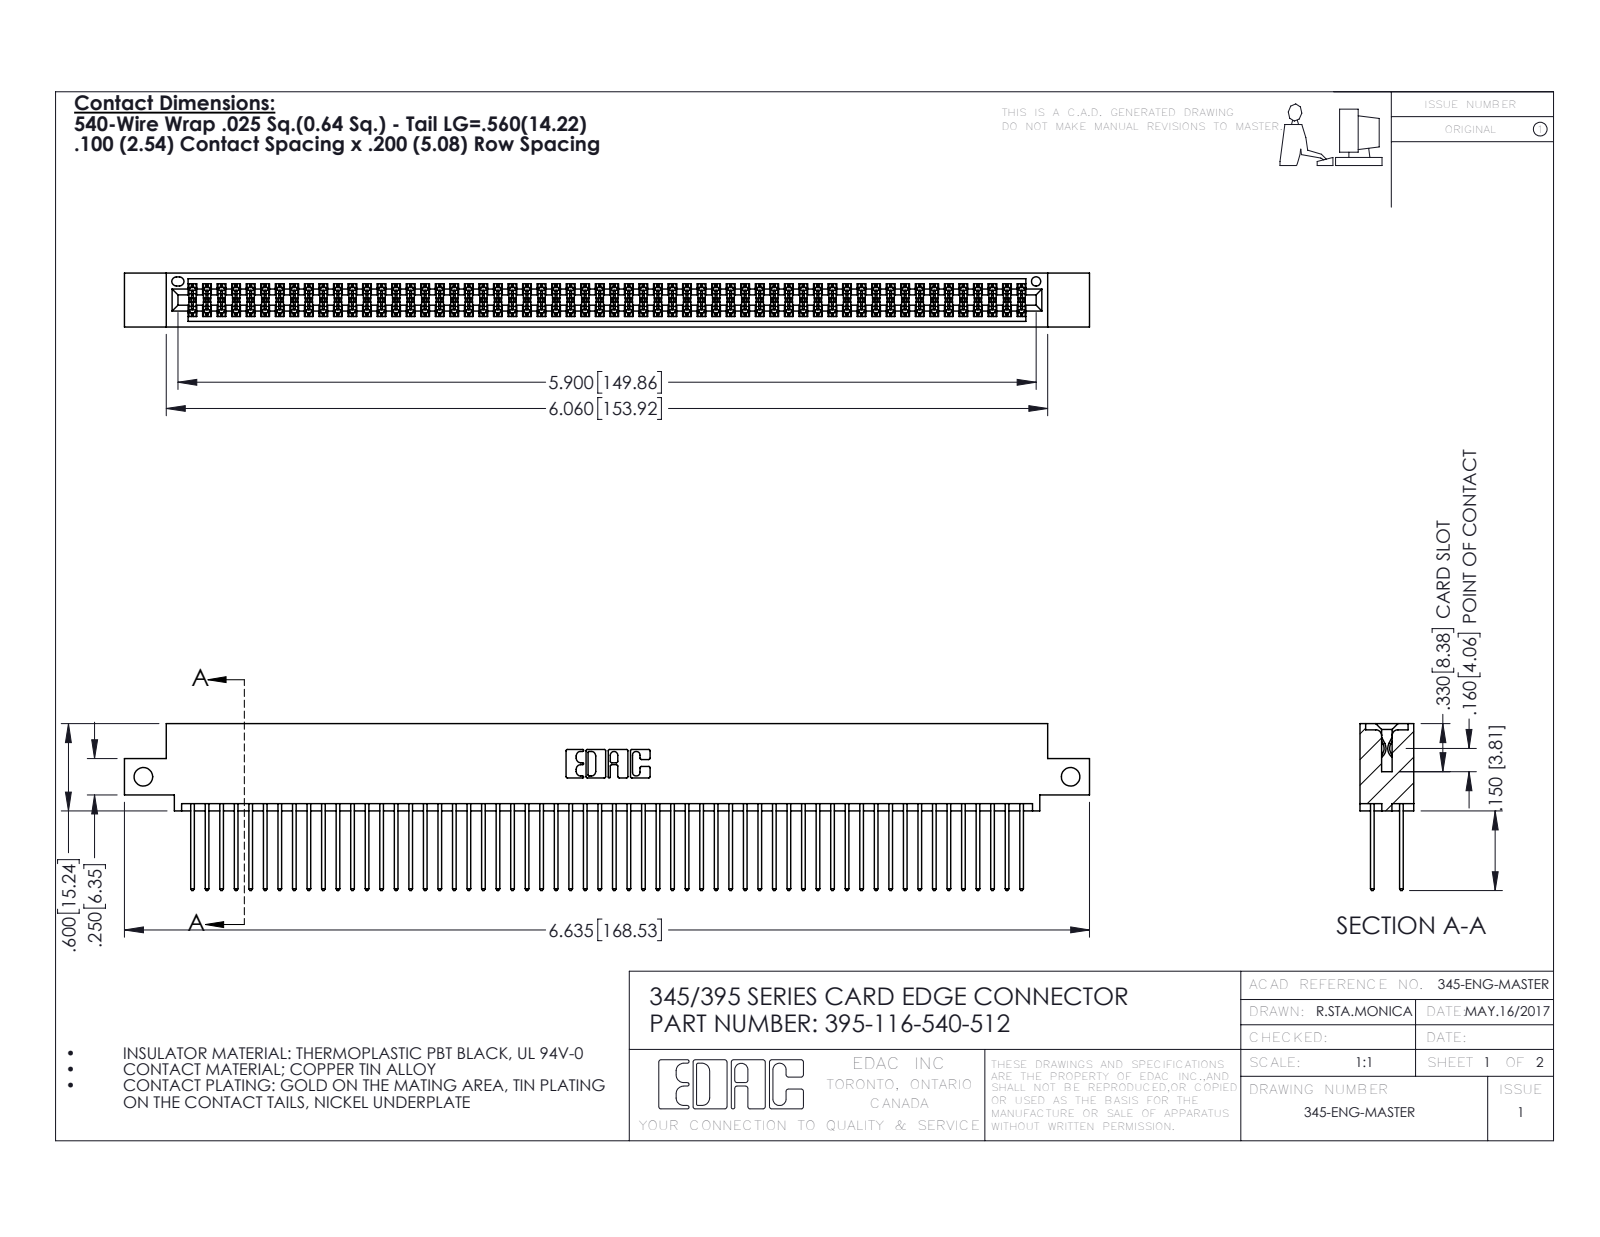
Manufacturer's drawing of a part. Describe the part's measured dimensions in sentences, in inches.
The part is named "395-116-540-512; 345 Part_0.110 Offset - Side Mount; 345-292-001_345-293-140". Its 3-D file was written by "SolidWorks 2016 (CONFIG_CONTROL_DESIGN)". It is 117 solids with 5930 faces: 3912 planar, 2018 cylindrical and 0 other. Overall it measures 6.635 by 1.147 by 0.37 inches. Its volume is 1.025 cubic inches and its surface area 42.06 square inches. Round holes: 2 of diameter 0.128, 1 of diameter 0.064. Partial cylindrical surfaces (rounded edges, fillets, slot ends): 174 of radius 0.006, 116 of radius 0.01, 22 of radius 0.01, 6 of radius 0.007, 6 of radius 0.031, 3 of radius 0.026, 2 of radius 0.014, 2 of radius 0.019. The main face-to-face distances are 0.072, 0.298, 0.2, 0.098, 0.272, 0.025, 0.225, 0.37, 0.175, 0.149. The hole center spacings are 6.375.
